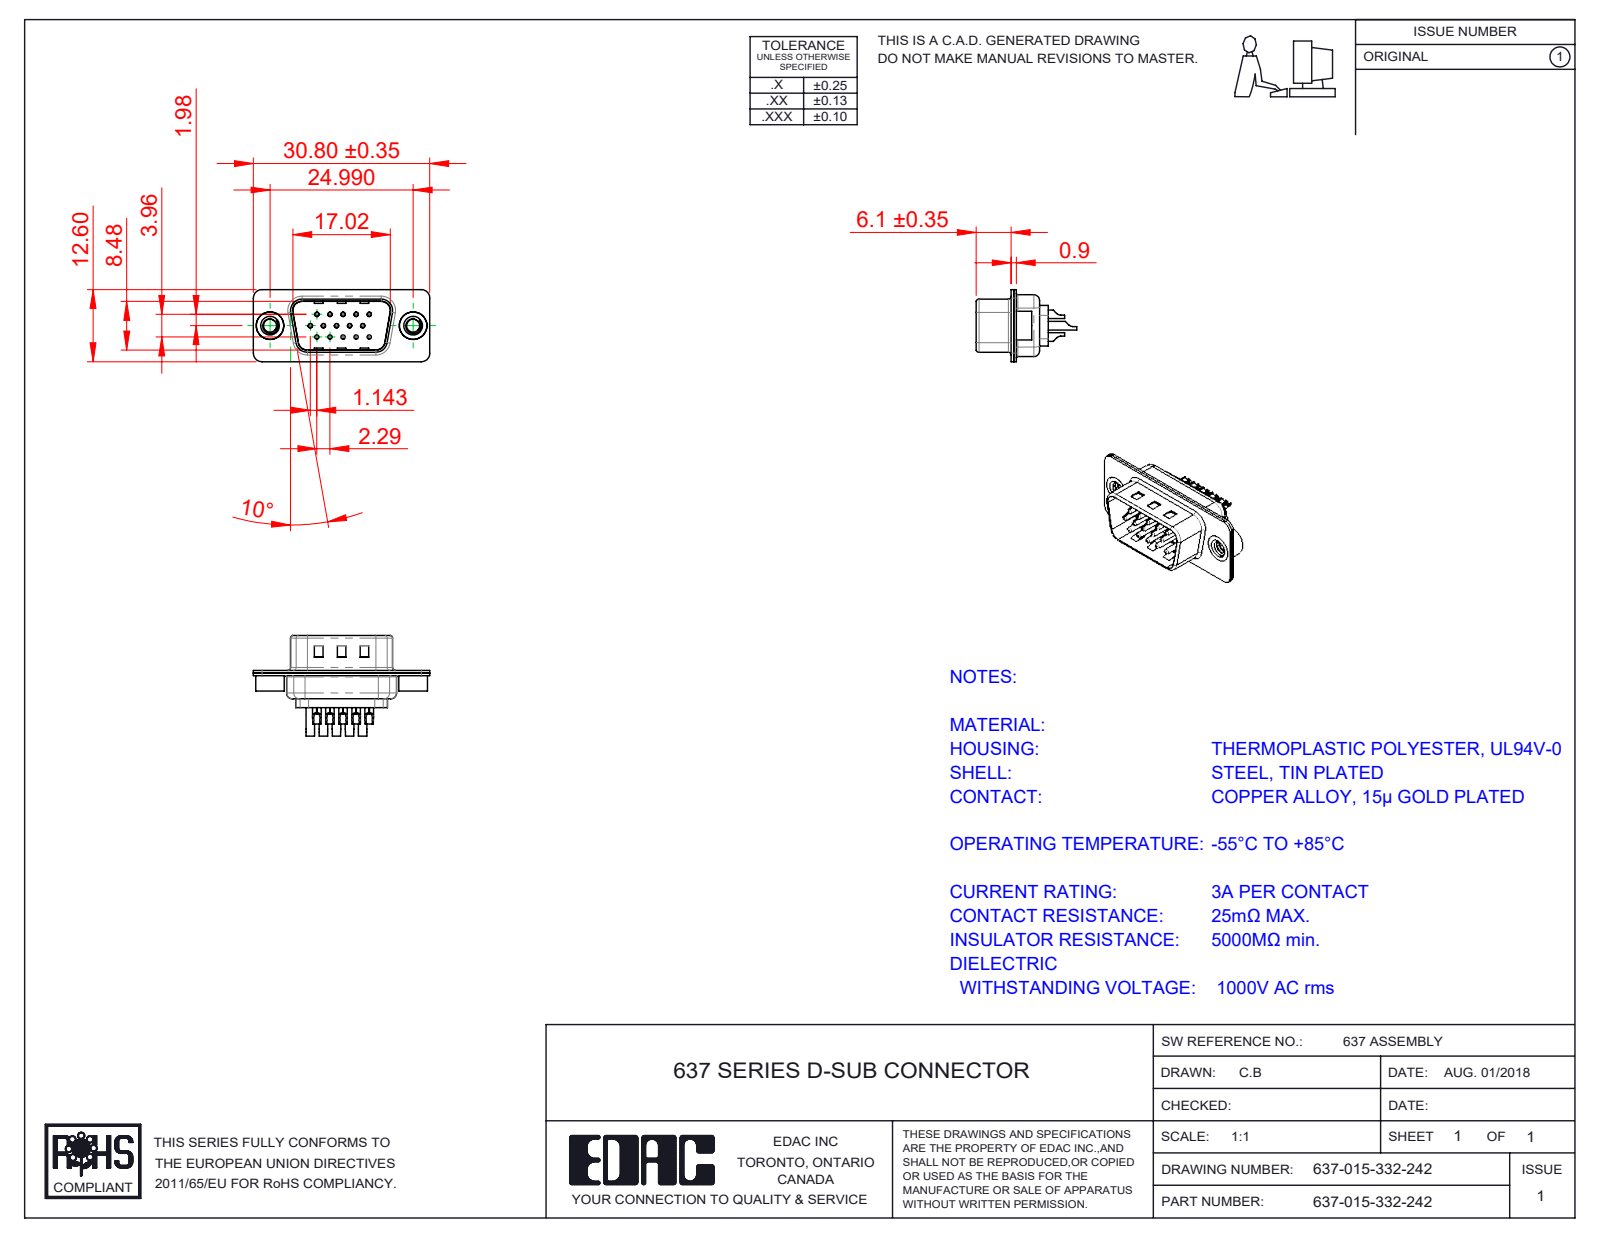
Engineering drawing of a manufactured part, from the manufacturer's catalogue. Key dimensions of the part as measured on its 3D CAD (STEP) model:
Part name (STEP PRODUCT): 637 Shell Front_15 Contacts; 637 4-40 Threaded Rivet; 637-015-332-242; 637 Contact Row 1_32 (+4 more)
STEP written by: SolidWorks 2020 (CONFIG_CONTROL_DESIGN)
Units: millimetres
Bodies: 20 solids, 1264 faces (317 planar, 564 cylindrical, 383 other)
Overall size (bounding box): 30.8 × 17.55 × 12.6
Volume: 1 332 mm³ · Surface area: 4 779 mm²
Round holes (diameter × count): ⌀0.35 ×15, ⌀1.1 ×15, ⌀1.6 ×15, ⌀2.26 ×2, ⌀4 ×2, ⌀4.8 ×2
Round bosses / shafts (diameter × count): ⌀2 ×15, ⌀1.5 ×15, ⌀0.75 ×15, ⌀5 ×2, ⌀4.9 ×2
Partial cylindrical surfaces — rounded edges, fillets, slot ends (radius × count): R1.5 ×16, R2 ×12, R0.5 ×8, R1 ×7, R0.25 ×4, R0.55 ×4, R0.7 ×4, R0.95 ×4
Main face-to-face distances: 0.45, 0.9, 0.4, 0.7, 8.88, 8.48, 1.05, 0.31, 4.55, 1.16
Hole centre spacings: 3.96, 2.28, 4.57, 2.29, 6.05, 6.86, 7.92, 6.04
